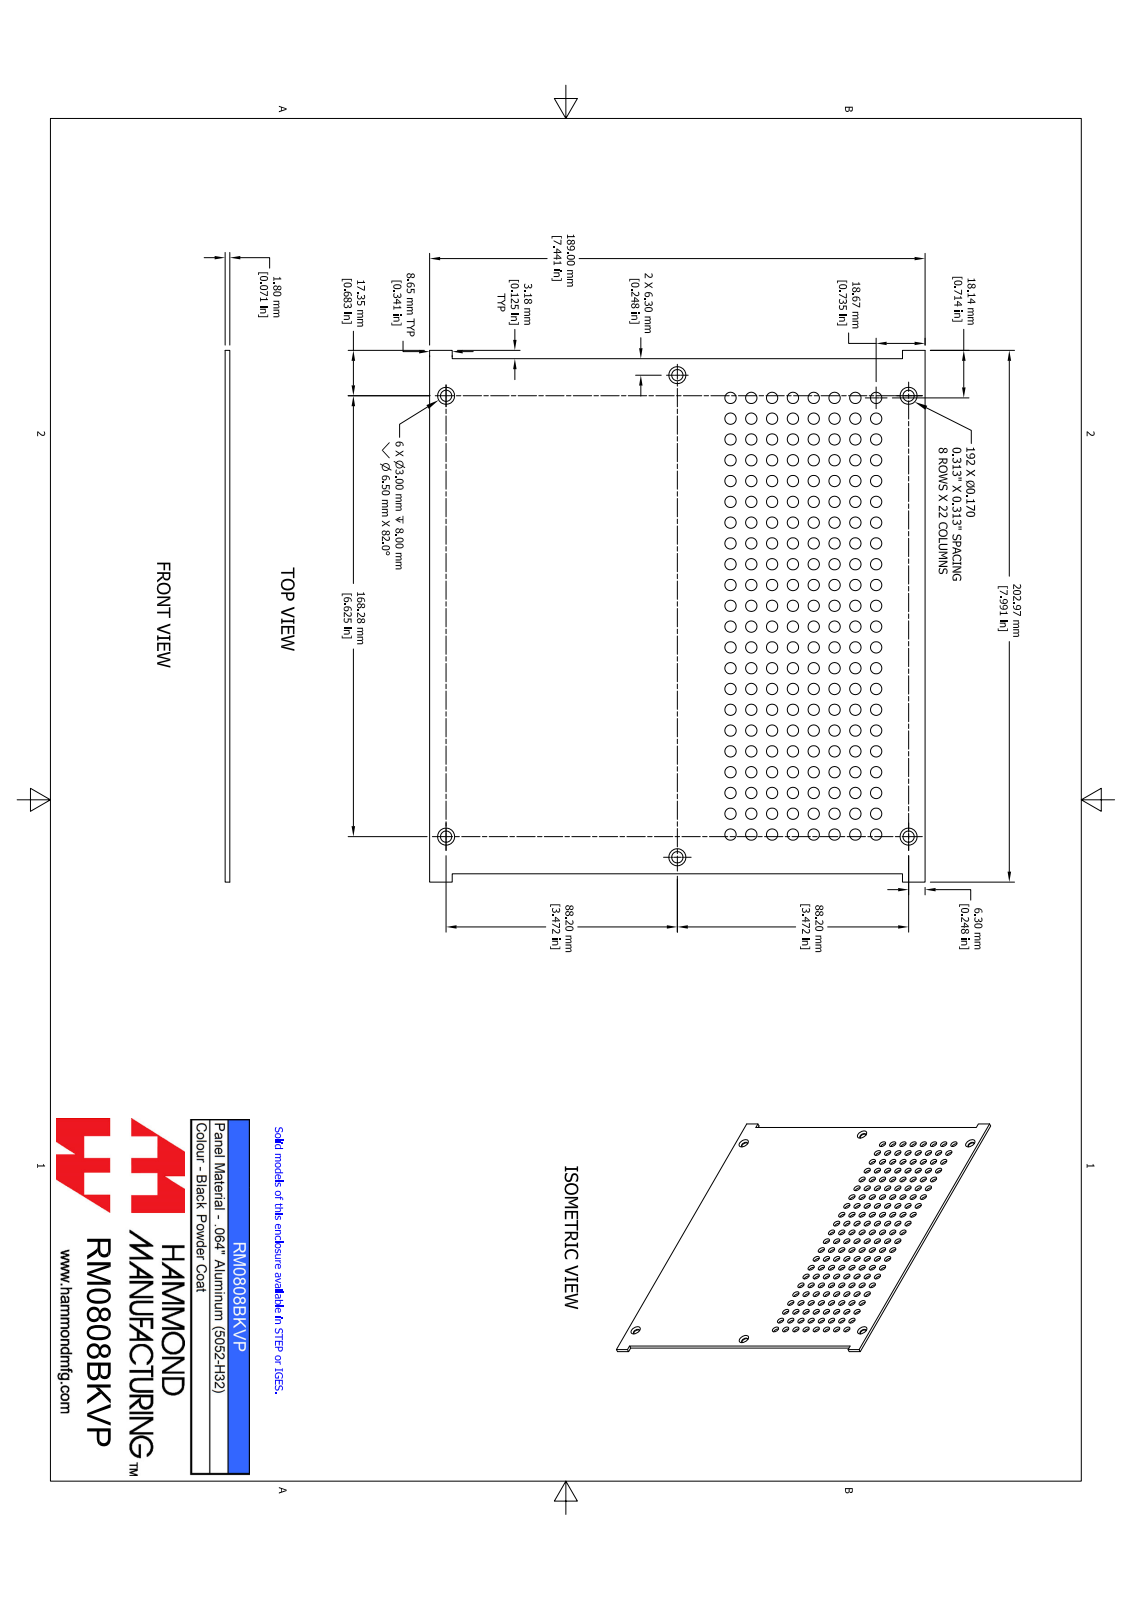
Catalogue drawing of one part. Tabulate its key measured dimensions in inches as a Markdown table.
| quantity | value |
| --- | --- |
| part name | RM0808BKVP |
| STEP written by | SolidWorks 2021 (AUTOMOTIVE_DESIGN) |
| units | inches |
| bodies | 1 solid, 202 faces (14 planar, 182 cylindrical, 6 other) |
| overall size | 7.991 × 7.441 × 0.071 |
| volume | 3.797 in³ |
| surface area | 116.3 in² |
| round holes (diameter × count) | 0.17 × 176, 0.169 × 6 |
| main face-to-face distances | 0.071, 7.441, 7.741, 0.125, 7.866, 7.991, 0.341, 7.1, 6.76 |
| hole center spacings | 0.313, 0.699, 1.289, 0.442, 0.988, 1.25, 0.625, 0.937 |
